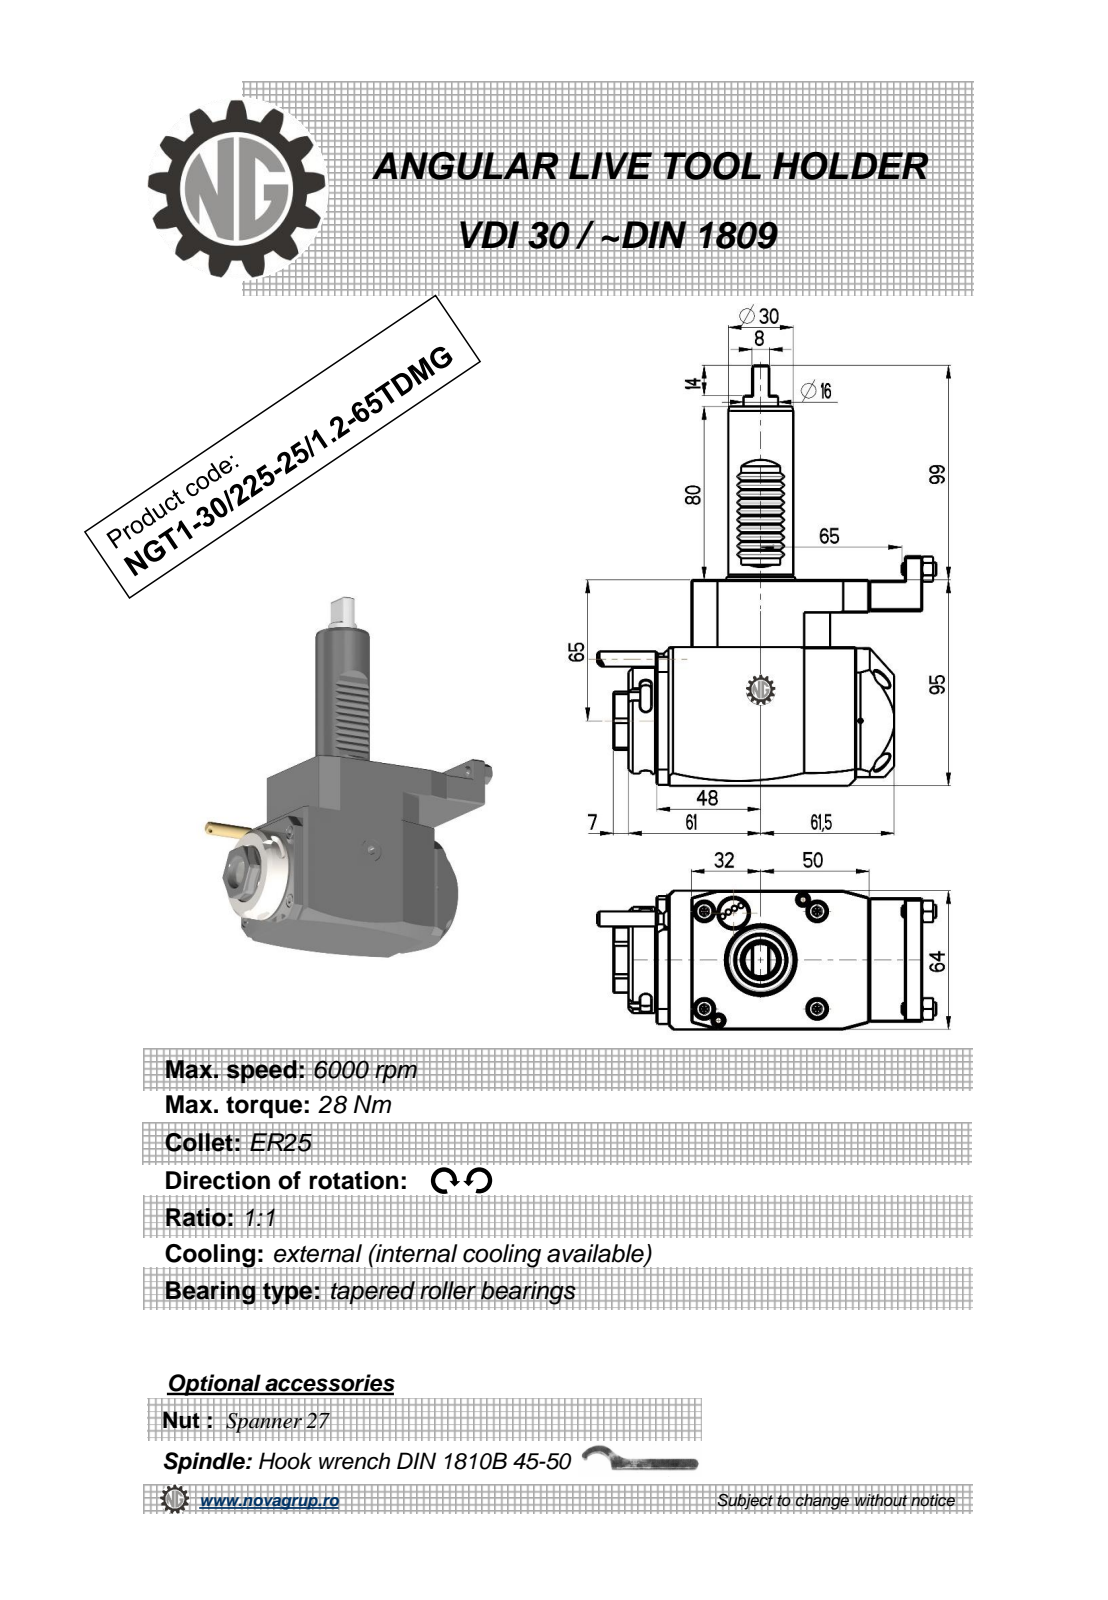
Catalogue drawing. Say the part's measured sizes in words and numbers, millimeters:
The part is named "NGT1_30_225_25_1_2_65TDMG". Its 3-D file was written by "PRO/ENGINEER BY PARAMETRIC TECHNOLOGY CORPORATION, 2010280 (CONFIG_CONTROL_DESIGN)". It is 1 solid with 359 faces: 193 planar, 72 cylindrical and 94 other. Overall it measures 194 by 156.38 by 64 millimeters. Its volume is 652 041 cubic millimeters and its surface area 61 656 square millimeters. Round holes: 1 of diameter 2.5, 1 of diameter 3, 1 of diameter 18. Round bosses or shafts: 2 of diameter 6, 1 of diameter 49, 1 of diameter 42, 1 of diameter 30, 1 of diameter 15.9, 1 of diameter 8, 1 of diameter 7, 1 of diameter 5. Partial cylindrical surfaces (rounded edges, fillets, slot ends): 10 of radius 0.3, 10 of radius 0.31, 6 of radius 2.5, 2 of radius 0.8, 2 of radius 180, 1 of radius 4.5, 1 of radius 15, 1 of radius 21.5. The main face-to-face distances are 64, 95, 16, 0.5, 13, 80, 122.5, 14.5, 80.5, 16.5. The hole center spacings are 34.25.
